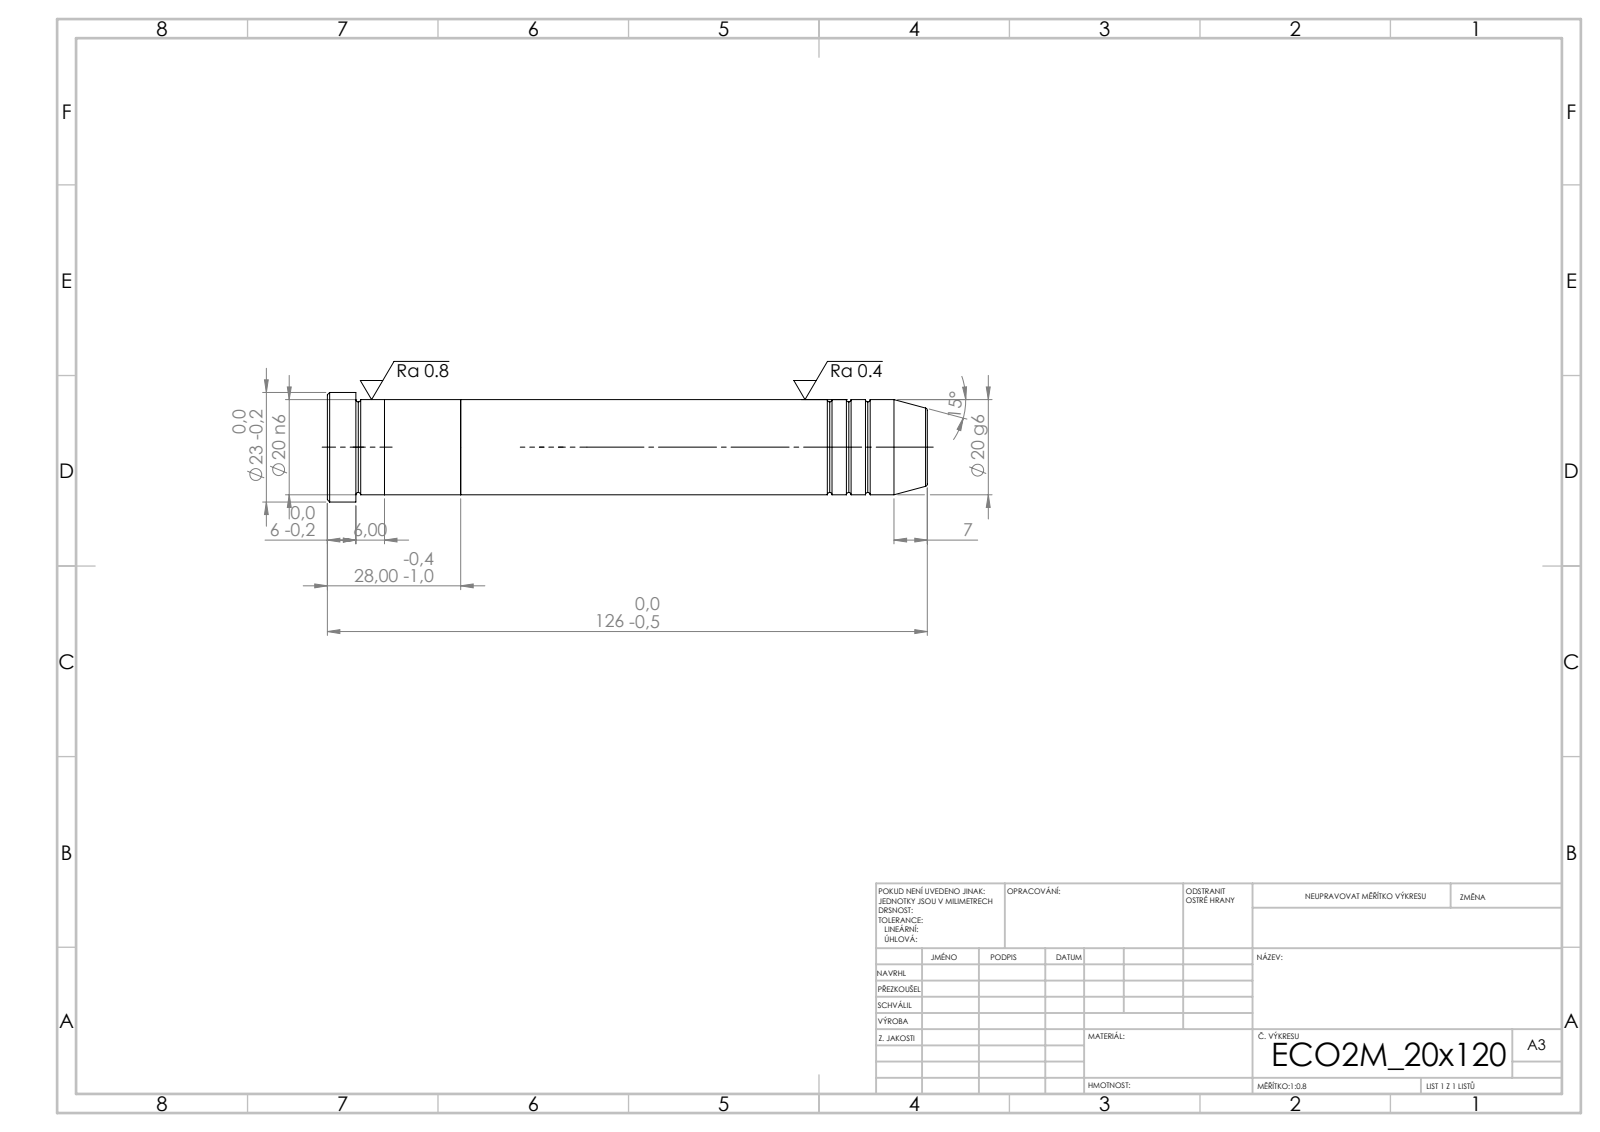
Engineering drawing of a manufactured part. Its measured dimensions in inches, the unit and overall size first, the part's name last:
Units: inches
Overall size (bounding box): 4.961 × 0.906 × 0.906
Round bosses / shafts (diameter × count): ⌀0.906 ×1, ⌀0.787 ×1
Main face-to-face distances: 0.63, 1.102, 0.472, 0.236, 3.858, 4.488, 4.961, 4.724, 0.866
Volume: 2.423 in³ · Surface area: 15.55 in²
Bodies: 3 solids, 43 faces (7 planar, 14 cylindrical, 22 other)
STEP written by: SolidWorks 2019 (CONFIG_CONTROL_DESIGN)
